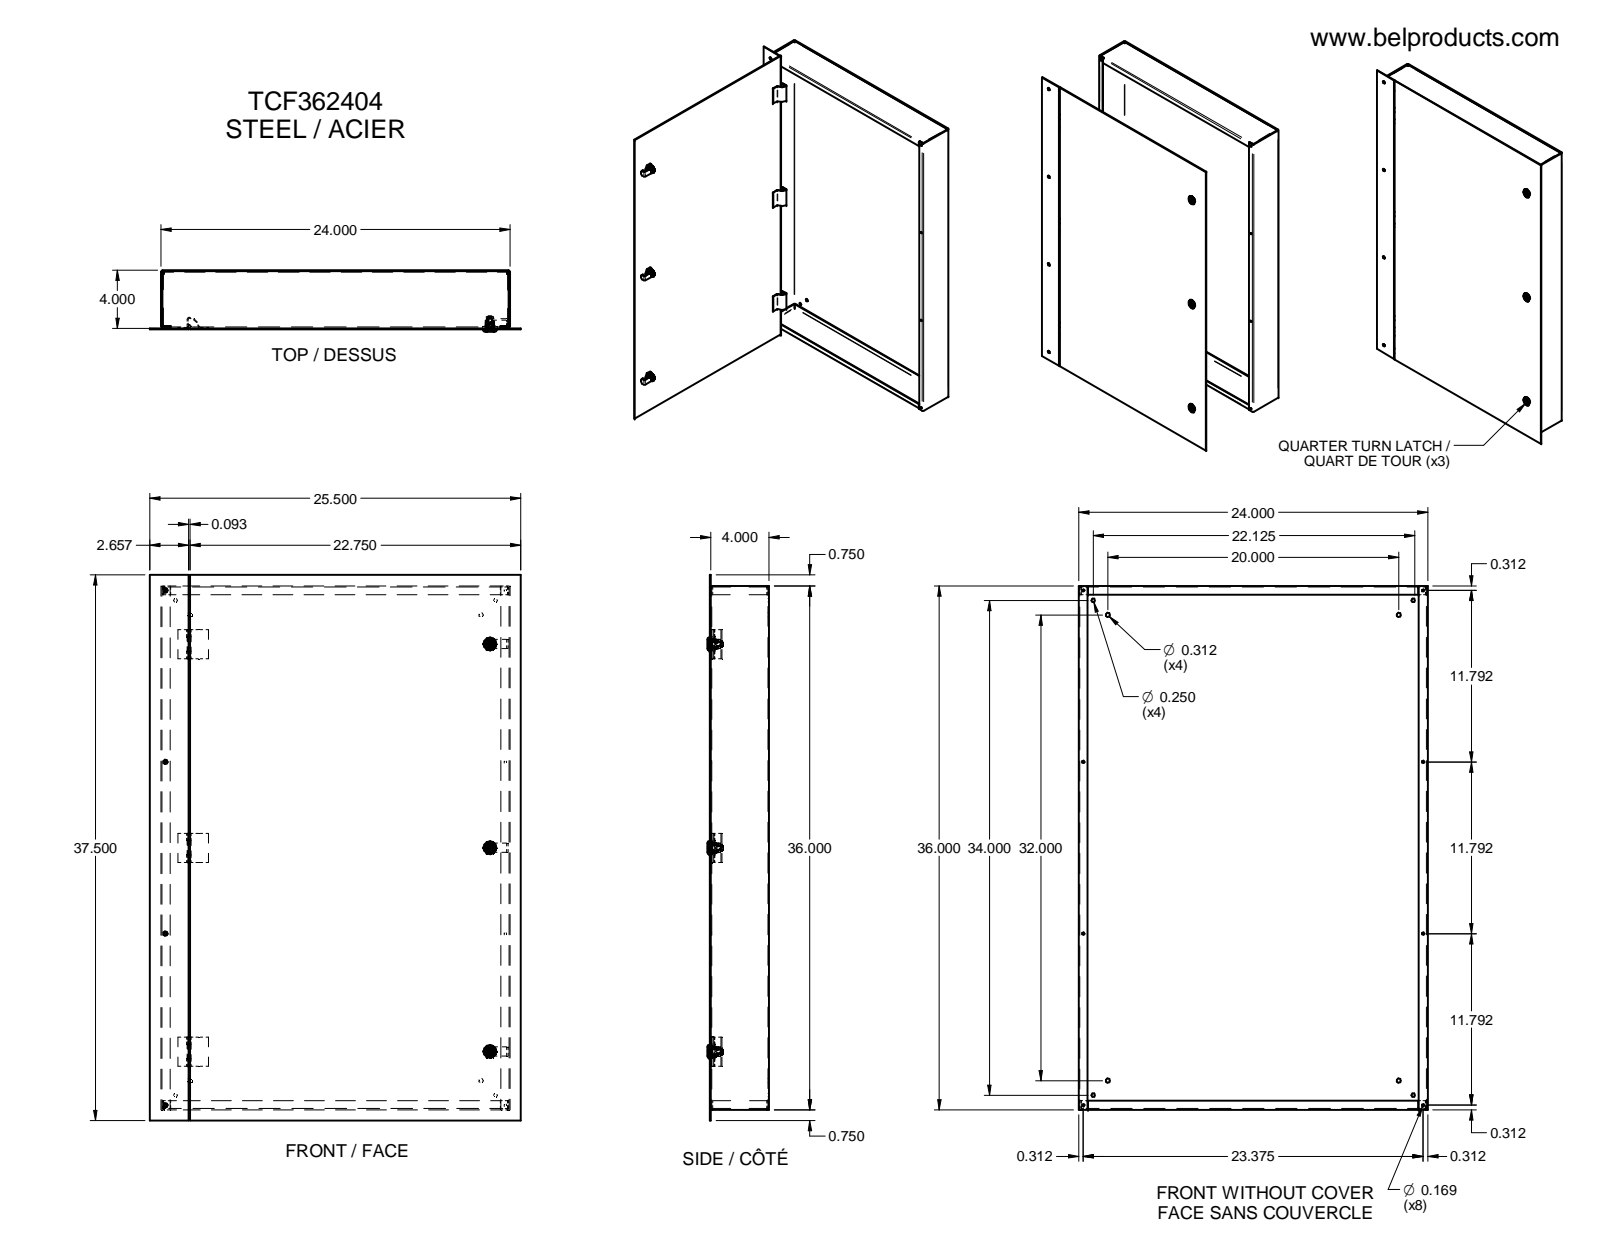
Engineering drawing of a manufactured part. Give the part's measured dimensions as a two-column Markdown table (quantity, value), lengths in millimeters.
| quantity | value |
| --- | --- |
| part name | LOCK AVEC TOURNEVIS TYPE 4-12 SANS CAME; HOSING-oa0; INSERT POUR TOURNEVIS-oa1; NOIX DE FIXATION-oa2 (+8 more) |
| STEP written by | Unknown (AUTOMOTIVE_DESIGN) |
| units | millimeters |
| bodies | 38 solids, 1559 faces (769 planar, 374 cylindrical, 416 other) |
| overall size | 952.5 × 647.7 × 107.97 |
| volume | 2 965 000 mm³ |
| surface area | 3 144 000 mm² |
| round holes (diameter × count) | 4.29 × 8, 7.92 × 8, 6.35 × 4, 6.99 × 3, 9.1 × 3, 11.18 × 3, 12.83 × 3, 15.8 × 3, 17.46 × 3, 3.81 × 1 |
| round bosses / shafts (diameter × count) | 22.86 × 3, 22.61 × 3, 15.75 × 3, 12.95 × 3, 12.62 × 3, 12.19 × 3, 11.86 × 3, 10.08 × 3 |
| partial cylindrical surfaces (radius × count) | 9.53 × 32, 0.25 × 24, 0.81 × 13, 2.72 × 12, 9.42 × 6, 6.22 × 3, 6.6 × 3, 6.99 × 3 |
| main face-to-face distances | 1.91, 101.6, 99.69, 103.51, 1.9, 607.69, 912.5, 609.6, 605.78, 101.59 |
| hole center spacings | 24.69, 35.92, 60.61, 260.2, 282.59, 299.51, 355.6, 534 |
